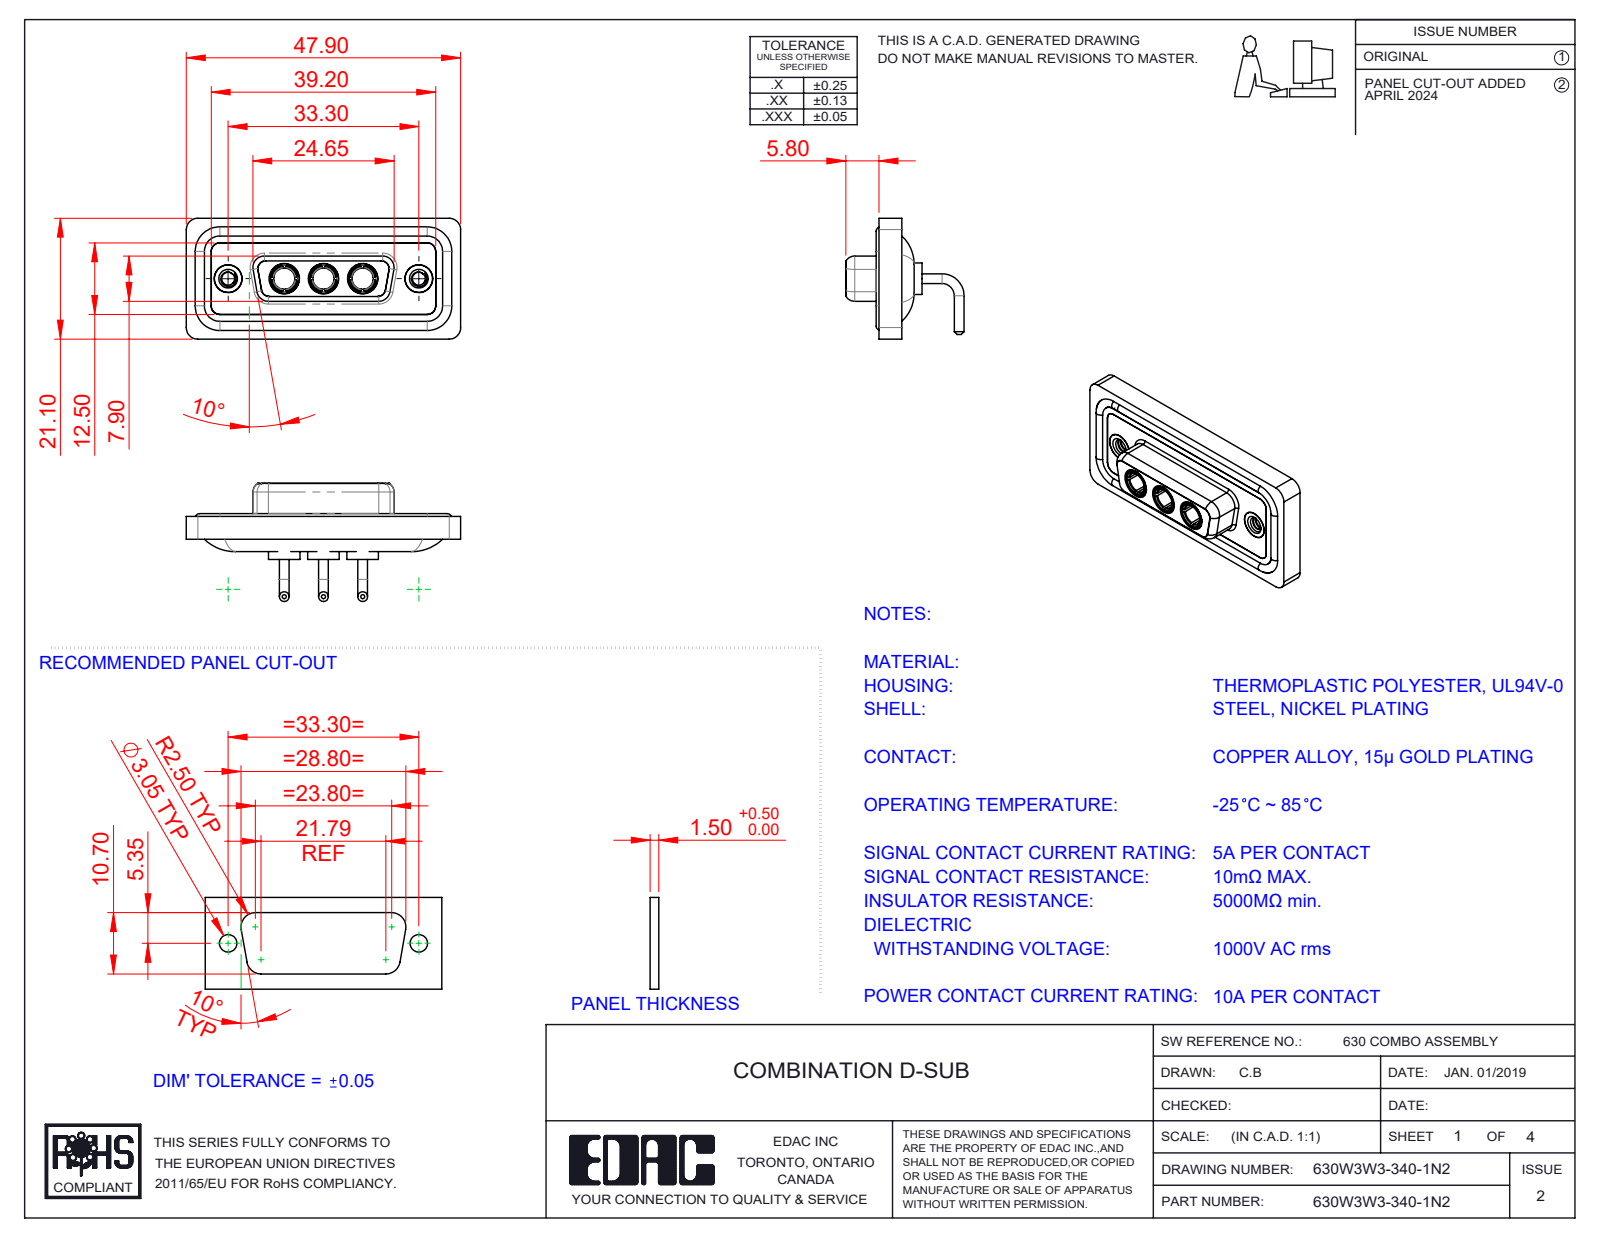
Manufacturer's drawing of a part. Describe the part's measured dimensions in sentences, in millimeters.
The part is named "Power Socket_10A RA; 630Combo Housing_3W3; 630Combo Threaded Rivet_2; 630Combo Waterproof Housing_15 Contacts (+3 more)". Its 3-D file was written by "SolidWorks 2023 (CONFIG_CONTROL_DESIGN)". It is 13 solids with 620 faces: 192 planar, 263 cylindrical and 165 other. Overall it measures 47.9 by 21.1 by 20.65 millimeters. Its volume is 6 006 cubic millimeters and its surface area 9 819 square millimeters. Round holes: 5 of diameter 4.85, 3 of diameter 3.7, 3 of diameter 5.3, 2 of diameter 2.26, 2 of diameter 4, 2 of diameter 4.05, 2 of diameter 5. Round bosses or shafts: 6 of diameter 1.7, 4 of diameter 1.6, 3 of diameter 5.5, 3 of diameter 5.2, 3 of diameter 4.96, 3 of diameter 4.75, 3 of diameter 3.75, 2 of diameter 4.95. Partial cylindrical surfaces (rounded edges, fillets, slot ends): 20 of radius 2, 18 of radius 1.5, 12 of radius 1.35, 8 of radius 1.6, 4 of radius 0.25, 4 of radius 0.5, 4 of radius 0.6, 4 of radius 0.65. The main face-to-face distances are 0.4, 1.8, 1.1, 1.6, 2.9, 2.5, 3.1, 3.7, 1.5, 4.1. The hole center spacings are 6.85, 9.8, 16.65, 23.5, 13.7, 33.3.
